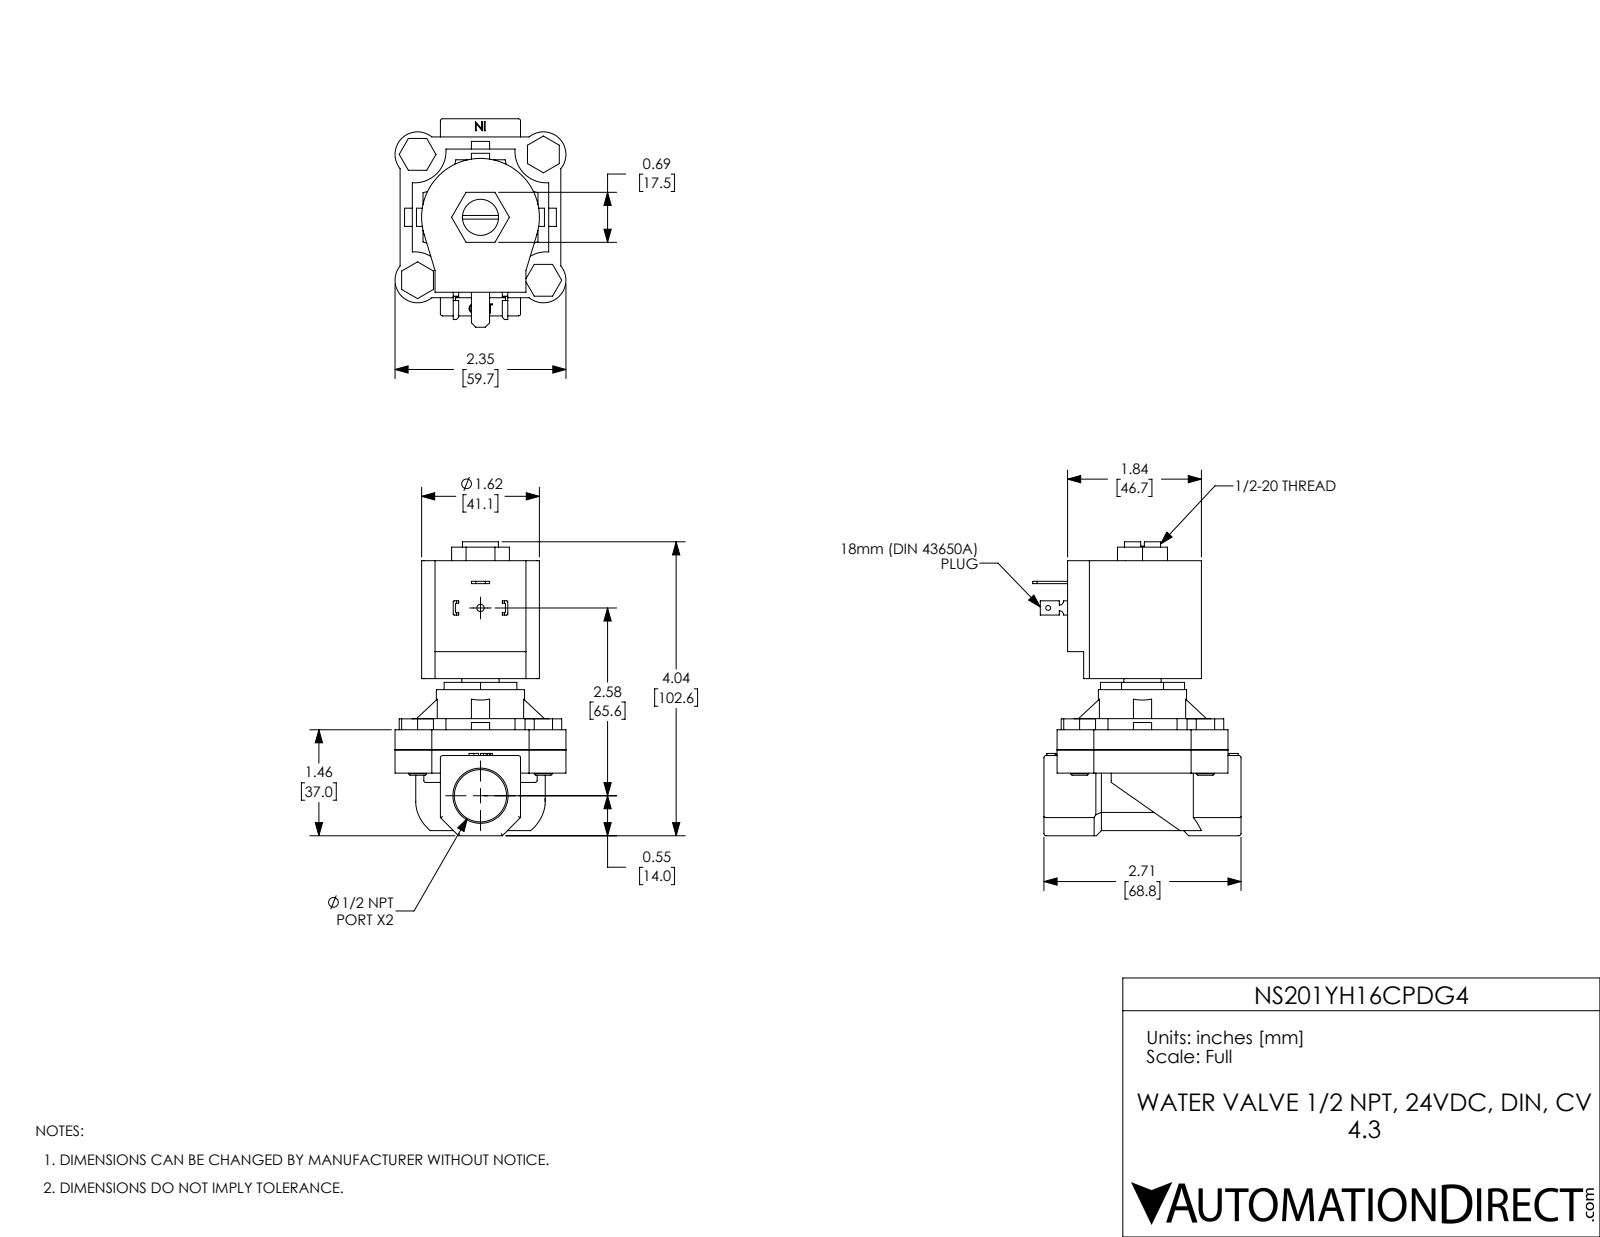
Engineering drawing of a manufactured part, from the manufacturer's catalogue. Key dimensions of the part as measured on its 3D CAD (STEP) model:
Part name (STEP PRODUCT): NS201YH16CPDG4
STEP written by: SolidWorks 2024 (CONFIG_CONTROL_DESIGN)
Units: inches
Bodies: 11 solids, 385 faces (239 planar, 113 cylindrical, 33 other)
Overall size (bounding box): 4.04 × 2.865 × 2.35
Volume: 10.1 in³ · Surface area: 67.71 in²
Round holes (diameter × count): ⌀0.25 ×4, ⌀0.067 ×1, ⌀0.1 ×1, ⌀0.496 ×1, ⌀0.512 ×1, ⌀0.719 ×1, ⌀1.155 ×1
Round bosses / shafts (diameter × count): ⌀0.248 ×4, ⌀1.213 ×1
Partial cylindrical surfaces — rounded edges, fillets, slot ends (radius × count): R0.03 ×15, R0.015 ×8, R0.31 ×4, R0.432 ×4, R0.579 ×4, R0.06 ×2, R0.81 ×1, R0.89 ×1
Main face-to-face distances: 0.276, 2.599, 2.323, 0.32, 0.596, 2.919, 0.554, 1.656, 0.25, 2.46
Hole centre spacings: 1.223, 1.73, 2.446, 2.581
